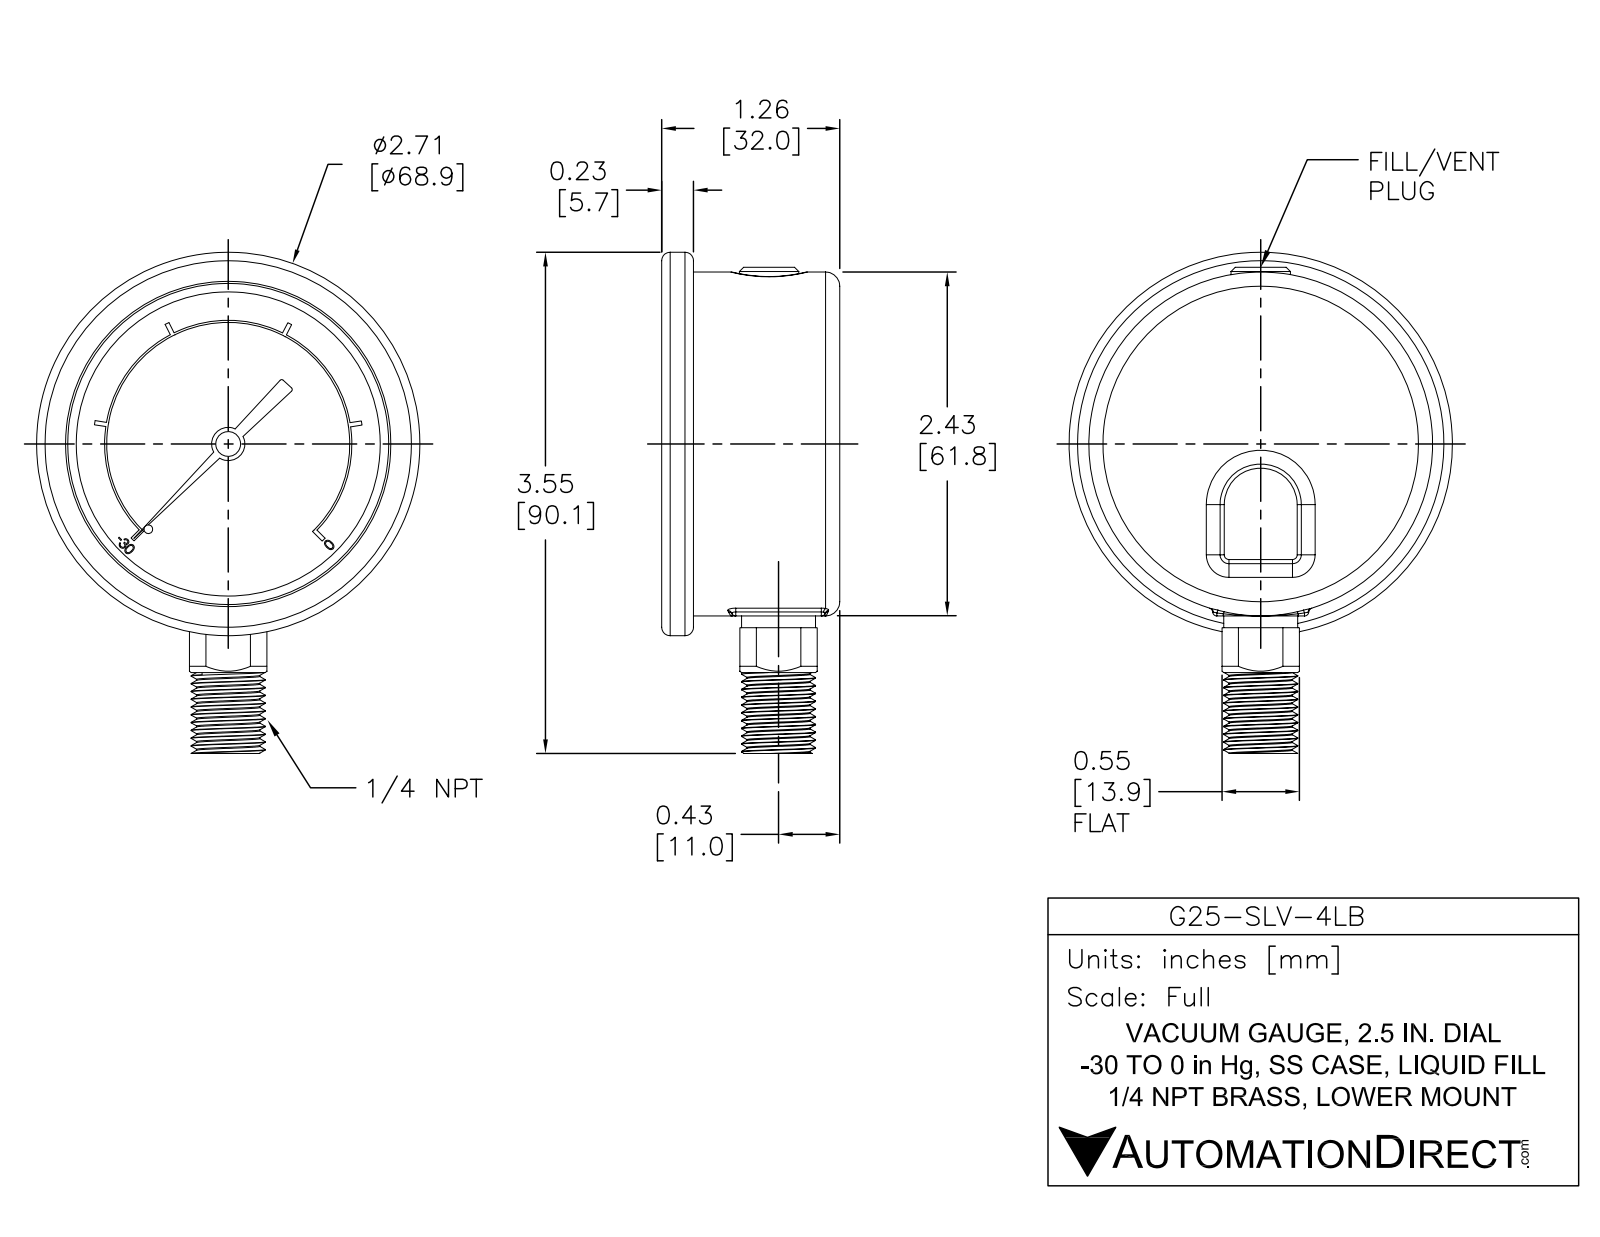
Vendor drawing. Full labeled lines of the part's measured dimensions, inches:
Part name (STEP PRODUCT): G25-SLV-4LB
STEP written by: SolidWorks 2021 (AUTOMOTIVE_DESIGN)
Units: inches
Bodies: 1 solid, 347 faces (195 planar, 85 cylindrical, 67 other)
Overall size (bounding box): 3.546 × 2.713 × 1.26
Volume: 5.273 in³ · Surface area: 24.68 in²
Round holes (diameter × count): ⌀0.027 ×1, ⌀0.071 ×1, ⌀0.119 ×1, ⌀2.272 ×1
Round bosses / shafts (diameter × count): ⌀2.713 ×1, ⌀2.433 ×1, ⌀0.524 ×1, ⌀0.42 ×1, ⌀0.235 ×1, ⌀0.176 ×1, ⌀0.14 ×1, ⌀0.041 ×1
Partial cylindrical surfaces — rounded edges, fillets, slot ends (radius × count): R0.03 ×9, R0.1 ×3, R0.015 ×2, R0.316 ×1, R0.86 ×1, R0.875 ×1
Main face-to-face distances: 1.01, 1.26, 0.25, 1.035, 0.025, 0.225, 0.1, 0.91, 0.935, 1.16
Hole centre spacings: 0.067
